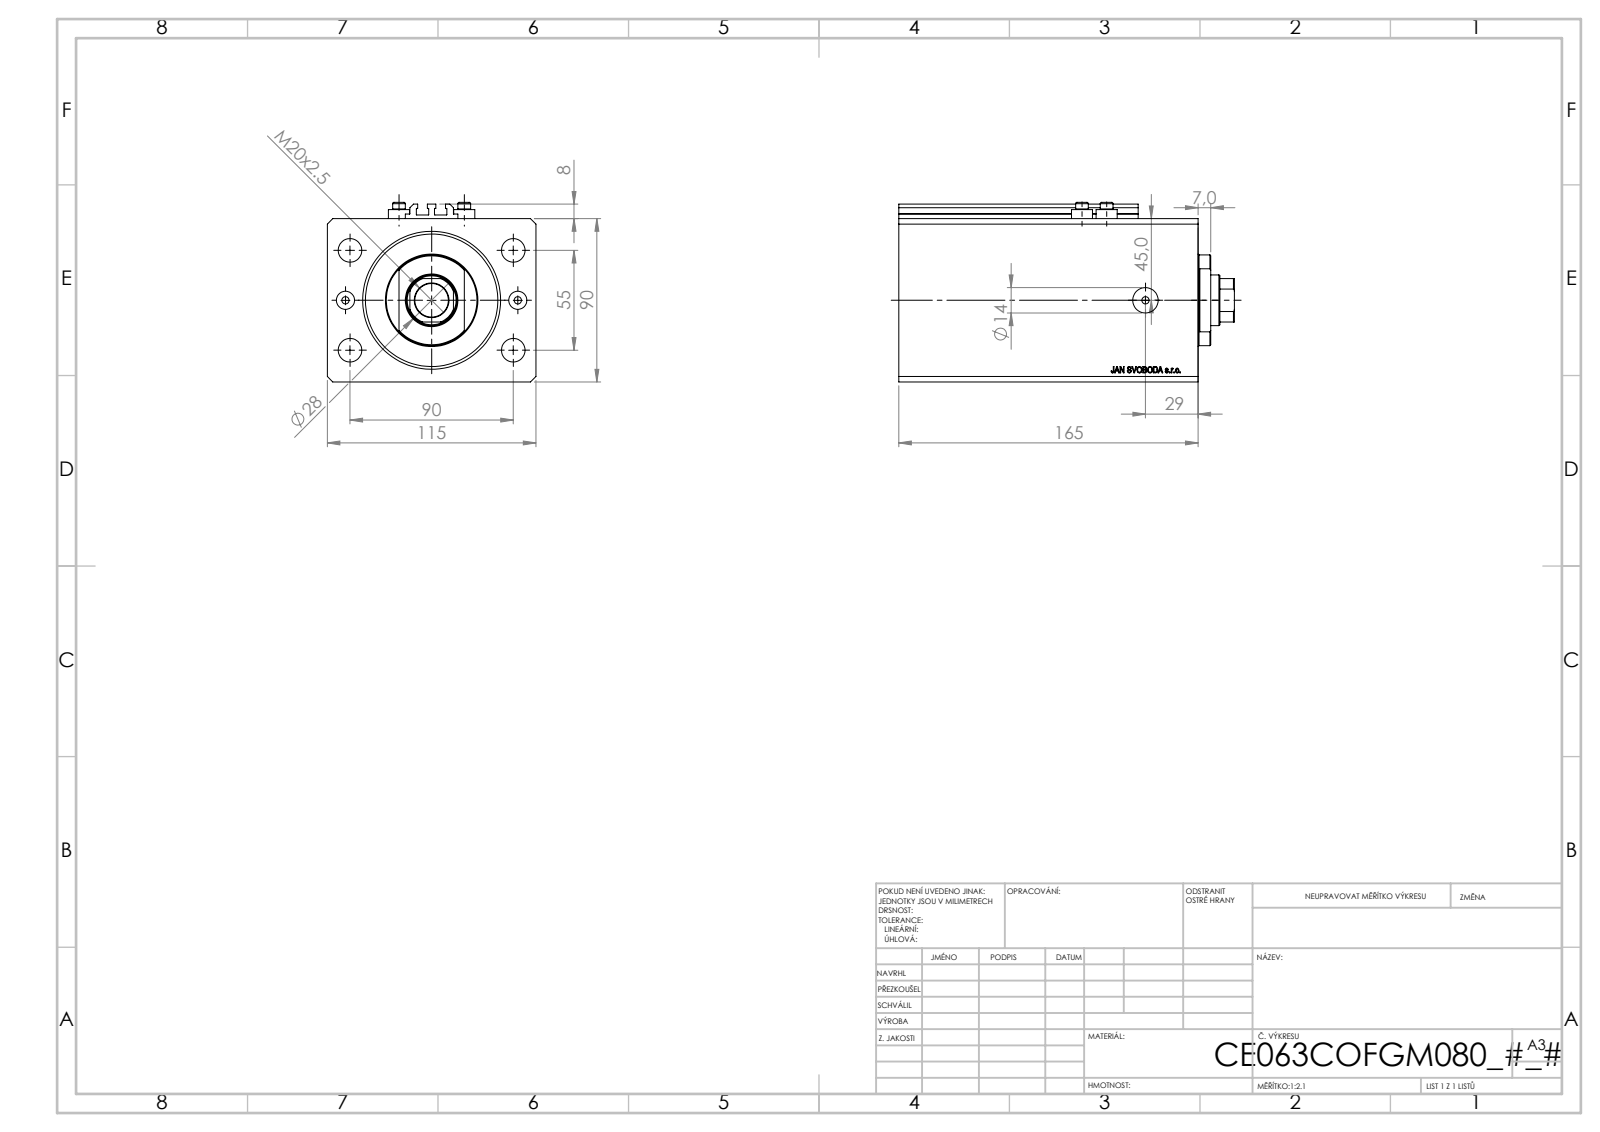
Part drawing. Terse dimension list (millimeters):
name: V250CE_C_VCP; ALLEN BOLT V250CE; V250CE_VC_C; V250CE_C_Body
written by: SolidWorks 2019 (CONFIG_CONTROL_DESIGN)
unit: mm
bodies: 8 solids, 1034 faces (504 planar, 86 cylindrical, 444 other)
size: 184.9 × 115 × 99
volume: 1 442 000 mm³; area: 207 485 mm²
holes: 8× ⌀4, 4× ⌀13, 2× ⌀10, 2× ⌀14, 1× ⌀18.5, 1× ⌀28, 1× ⌀63, 1× ⌀76
bosses: 4× ⌀11.6, 4× ⌀7, 1× ⌀50
rounds: 10× R0.2, 1× R13.5
face distances: 90, 115, 165, 17.9, 147.1, 134.9, 117, 30.1, 54.9, 80
hole spacings: 27.61, 52.74, 96.5, 13.6, 36, 38.48, 47.5, 55
